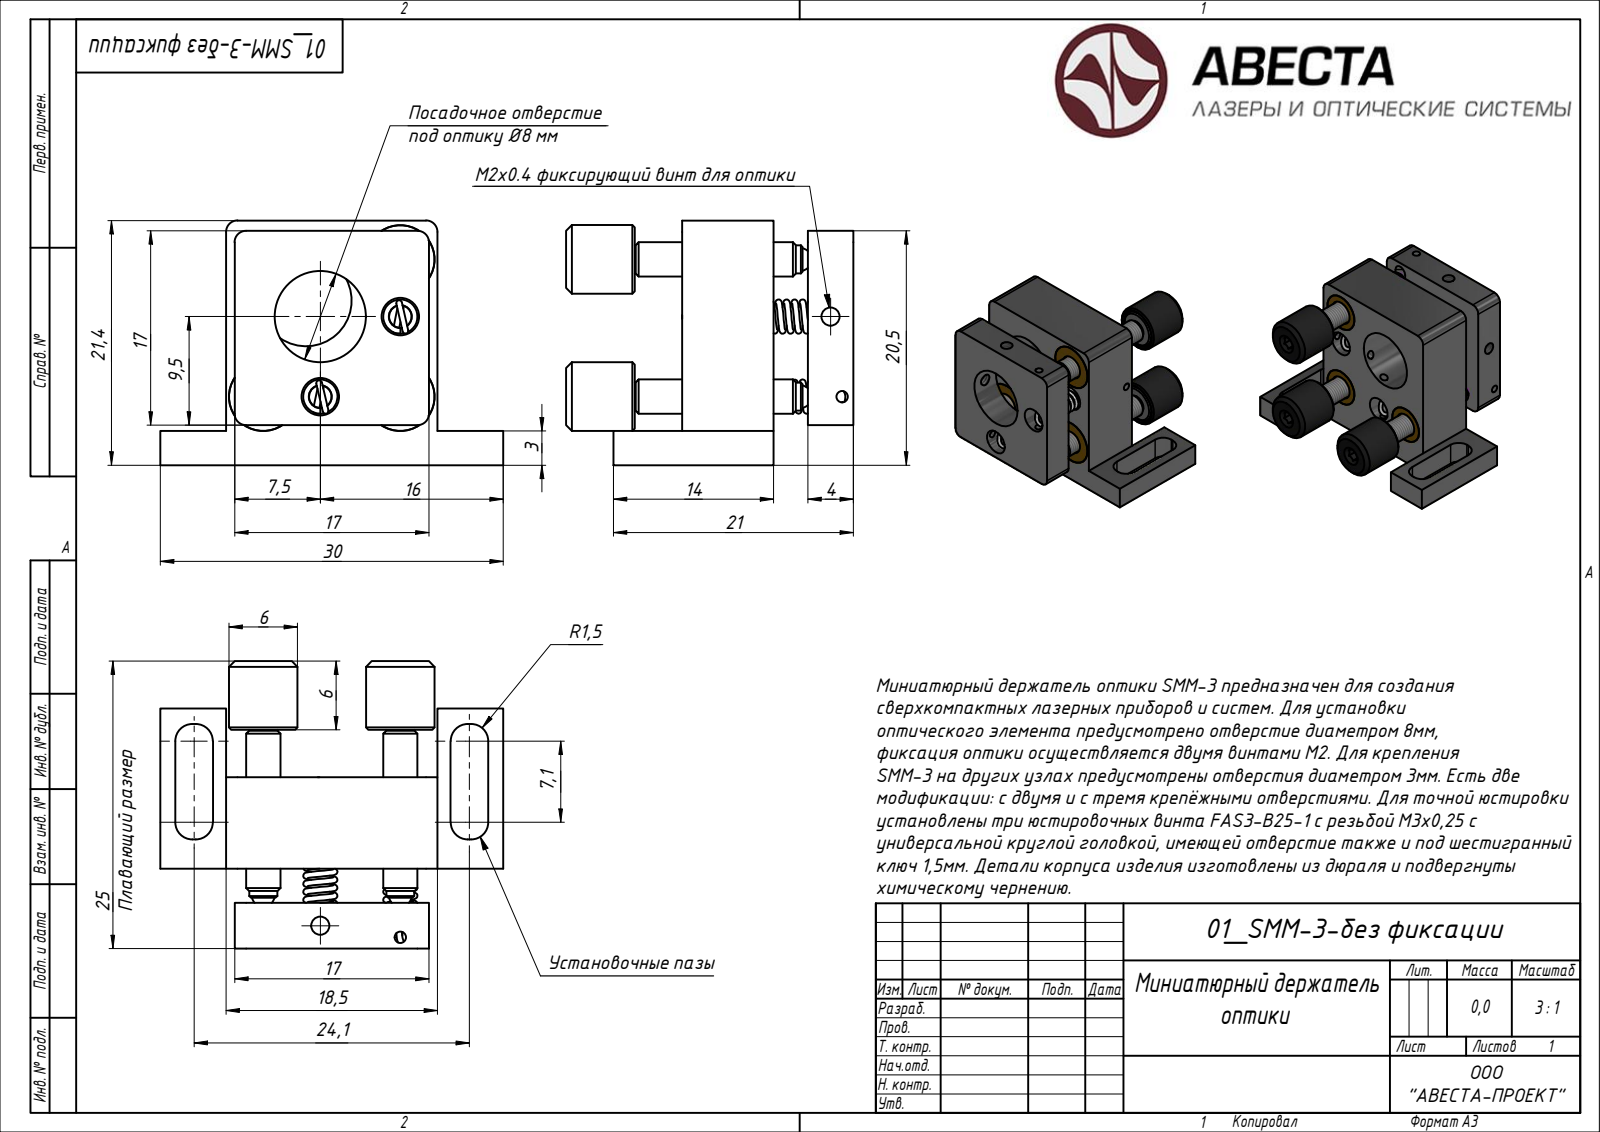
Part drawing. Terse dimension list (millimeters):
written by: ST-DEVELOPER v15 (AUTOMOTIVE_DESIGN)
unit: mm
bodies: 15 solids, 318 faces (81 planar, 0 cylindrical, 237 other)
size: 30 × 25.15 × 21.4
volume: 4 418 mm³; area: 5 986 mm²
face distances: 3, 8, 4, 15, 7, 11, 18.5, 17, 21.4, 6
